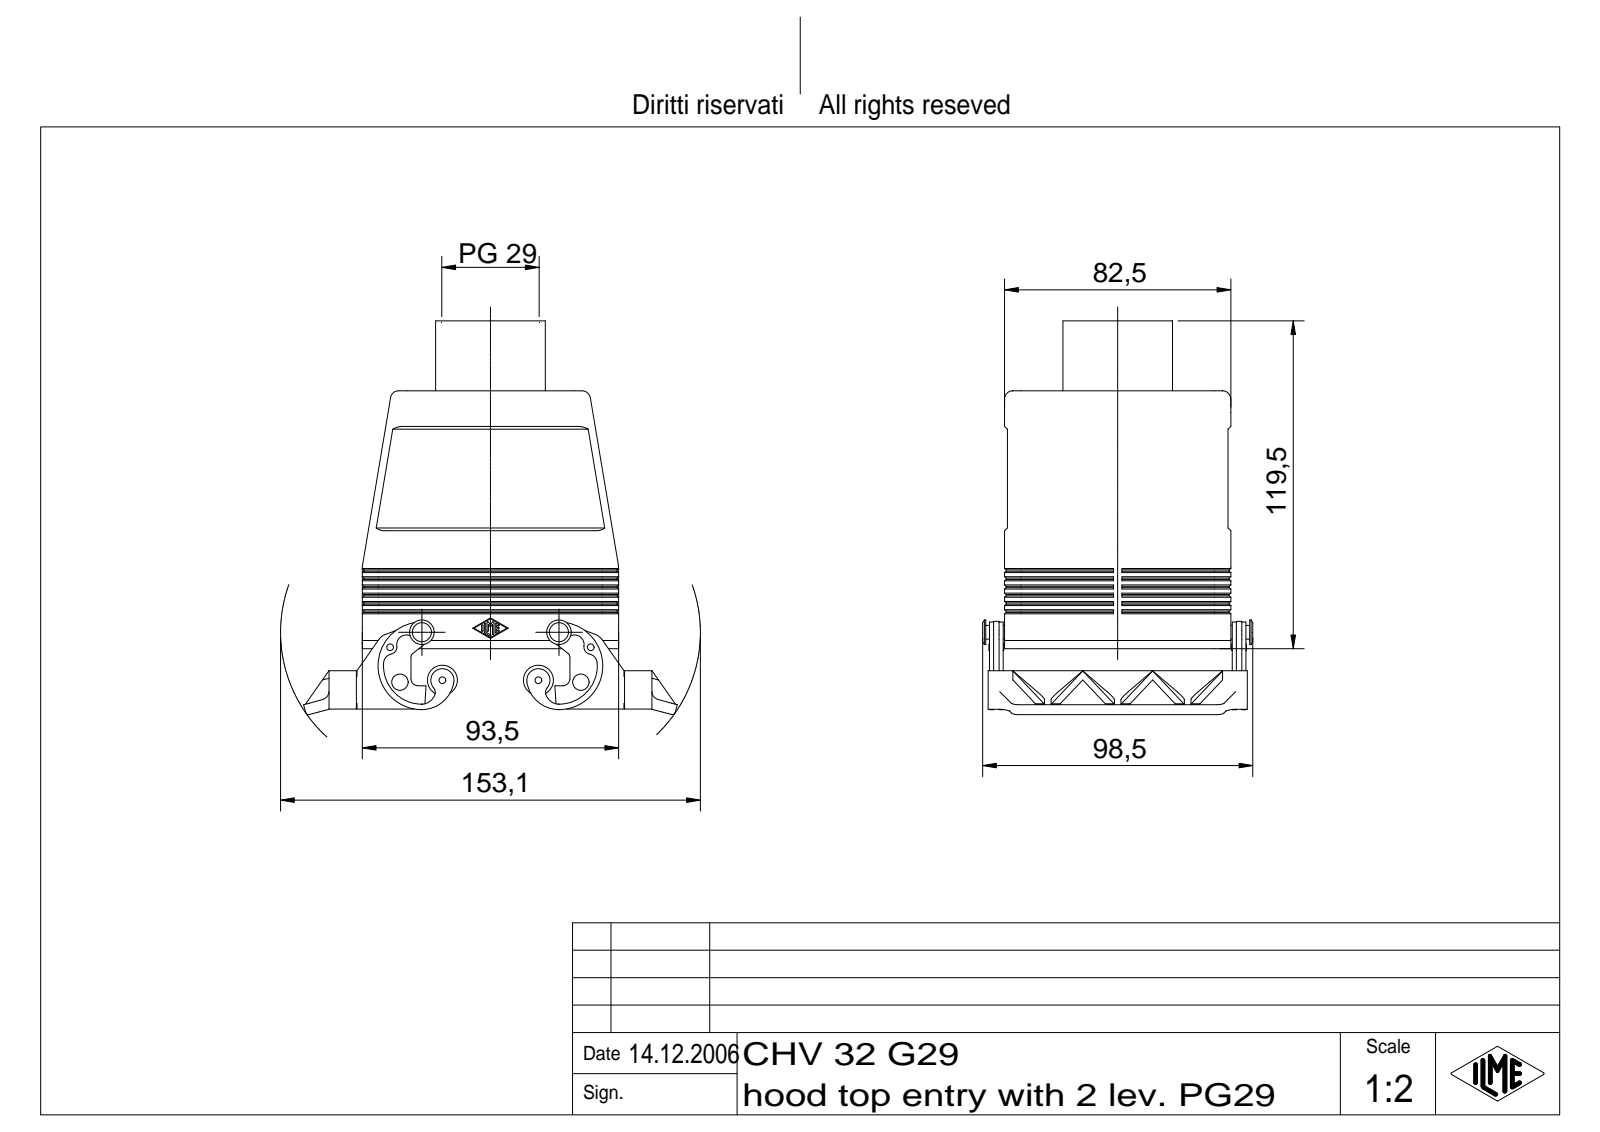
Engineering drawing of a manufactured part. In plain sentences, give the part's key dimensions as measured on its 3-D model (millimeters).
The part is named "CHV 32 G29". Its 3-D file was written by "Autodesk Inventor 7 (AUTOMOTIVE_DESIGN)". It is 1 solid with 1089 faces: 328 planar, 298 cylindrical and 463 other. Overall it measures 143.53 by 136.28 by 98.5 millimeters. Its volume is 187 453 cubic millimeters and its surface area 102 171 square millimeters. Round holes: 4 of diameter 2.46, 4 of diameter 3.5, 2 of diameter 2.5, 2 of diameter 6, 1 of diameter 33.48, 1 of diameter 35.48, 1 of diameter 51. Round bosses or shafts: 2 of diameter 11, 2 of diameter 9, 2 of diameter 5, 2 of diameter 2, 1 of diameter 65, 1 of diameter 49, 1 of diameter 48, 1 of diameter 40. Partial cylindrical surfaces (rounded edges, fillets, slot ends): 14 of radius 0.25, 14 of radius 3, 12 of radius 2, 10 of radius 6, 6 of radius 1, 6 of radius 2.5, 4 of radius 3.5, 4 of radius 5. The main face-to-face distances are 4, 82.5, 78.5, 74.5, 3, 1, 71.5, 11, 77.5, 81.5. The hole center spacings are 13.21, 27, 38.96, 49.62, 70.75, 77.5, 82.07, 66.
